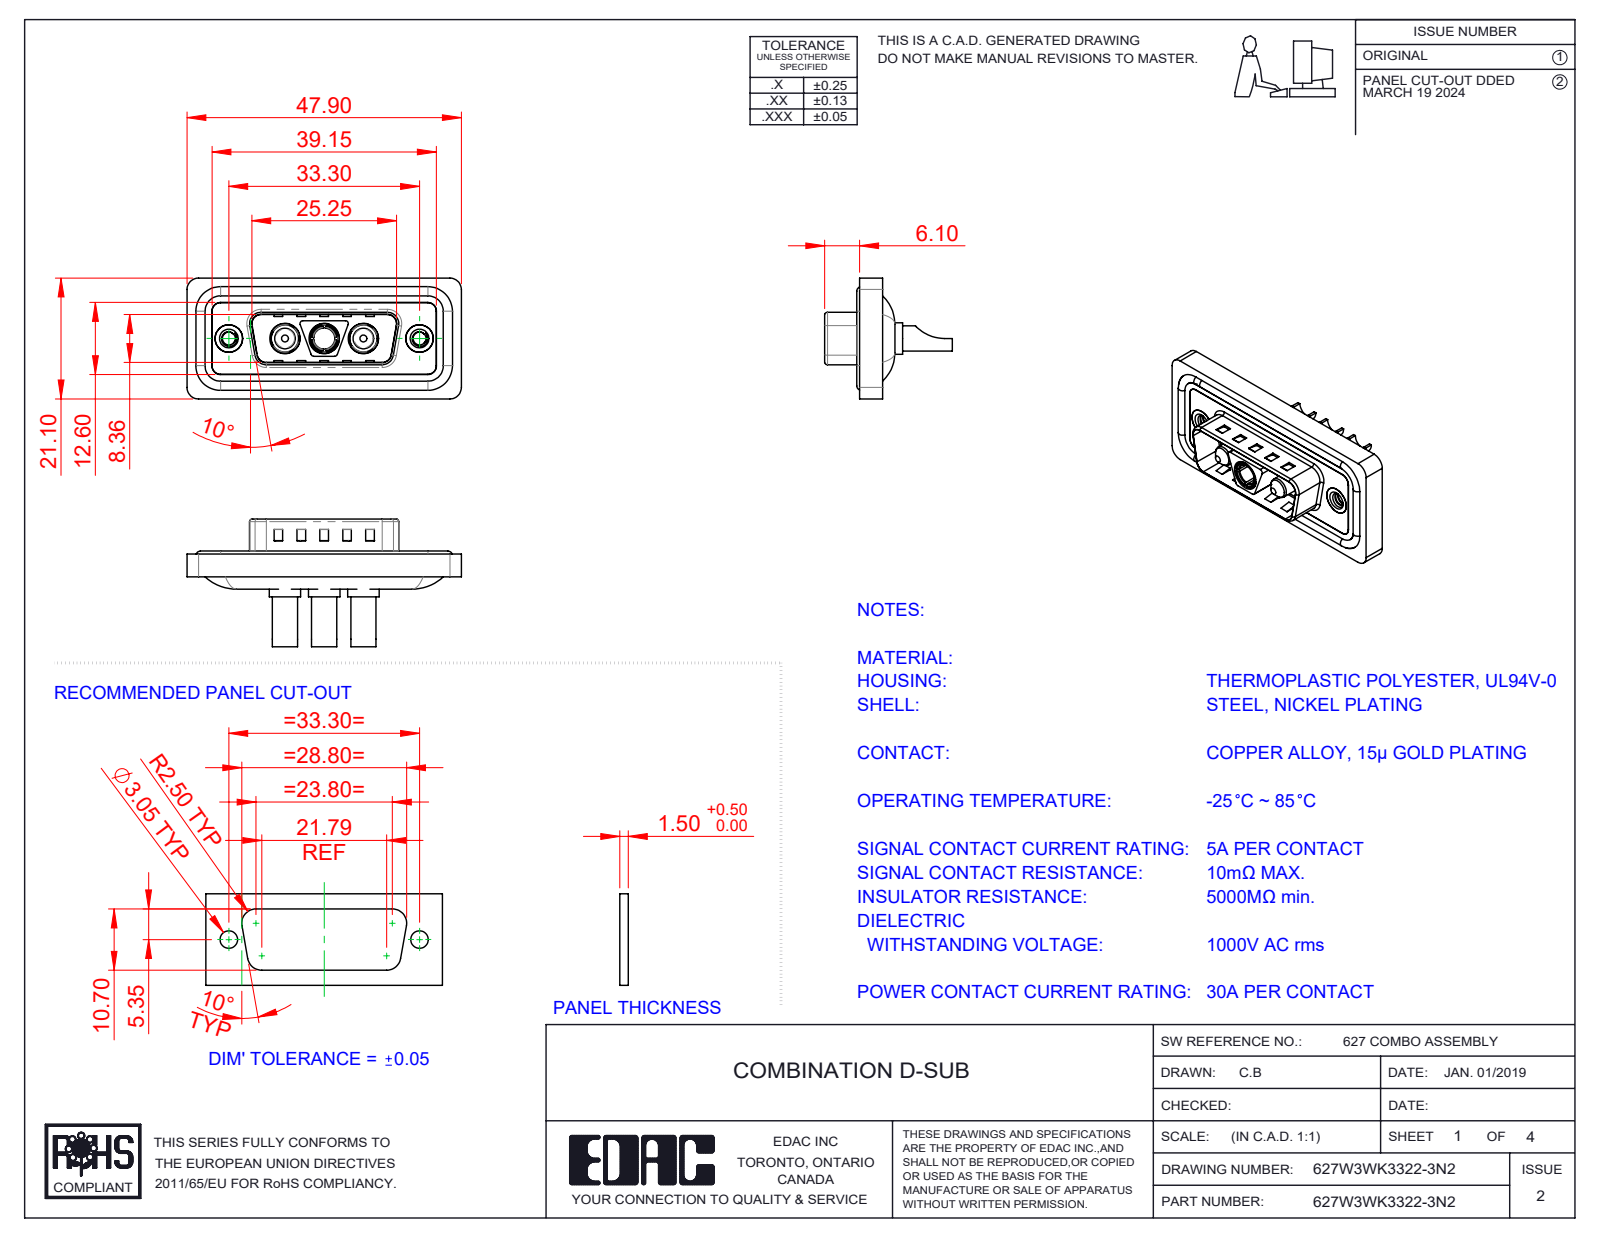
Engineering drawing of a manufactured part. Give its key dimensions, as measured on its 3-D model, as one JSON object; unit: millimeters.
{"part_name": "627Combo Threaded Rivet_2; Power Socket_30A SC; 627Combo Shell Rear_15 Contacts; 627Combo Shell Front_15 Contacts (+4 more)", "step_written_by": "SolidWorks 2023 (CONFIG_CONTROL_DESIGN)", "units": "millimeters", "bodies": {"solids": 13, "faces": 627, "planar": 240, "cylindrical": 259, "other": 128}, "overall_size": [47.9, 22.3, 21.1], "volume_mm3": 5760, "surface_area_mm2": 9450, "round_holes": [[3.5, 3], [4.85, 3], [5.3, 3], [2.26, 2], [4, 2], [4.8, 2], [5, 2], [3.7, 1]], "round_bosses_or_shafts": [[1.6, 4], [5.5, 3], [5.2, 3], [4.75, 3], [4.4, 3], [3.75, 3], [4.9, 2], [3.6, 2]], "partial_cylinders_radius": [[1.5, 26], [2, 20], [0.5, 12], [1.6, 8], [0.25, 4], [0.6, 4], [0.65, 4], [0.9, 4]], "face_to_face_distances": [0.4, 1.1, 0.5, 1.6, 3.1, 1.5, 2.9, 0.82, 9.58, 2.5], "hole_center_spacings": [6.85, 9.8, 16.65, 23.5, 13.7, 33.3]}
